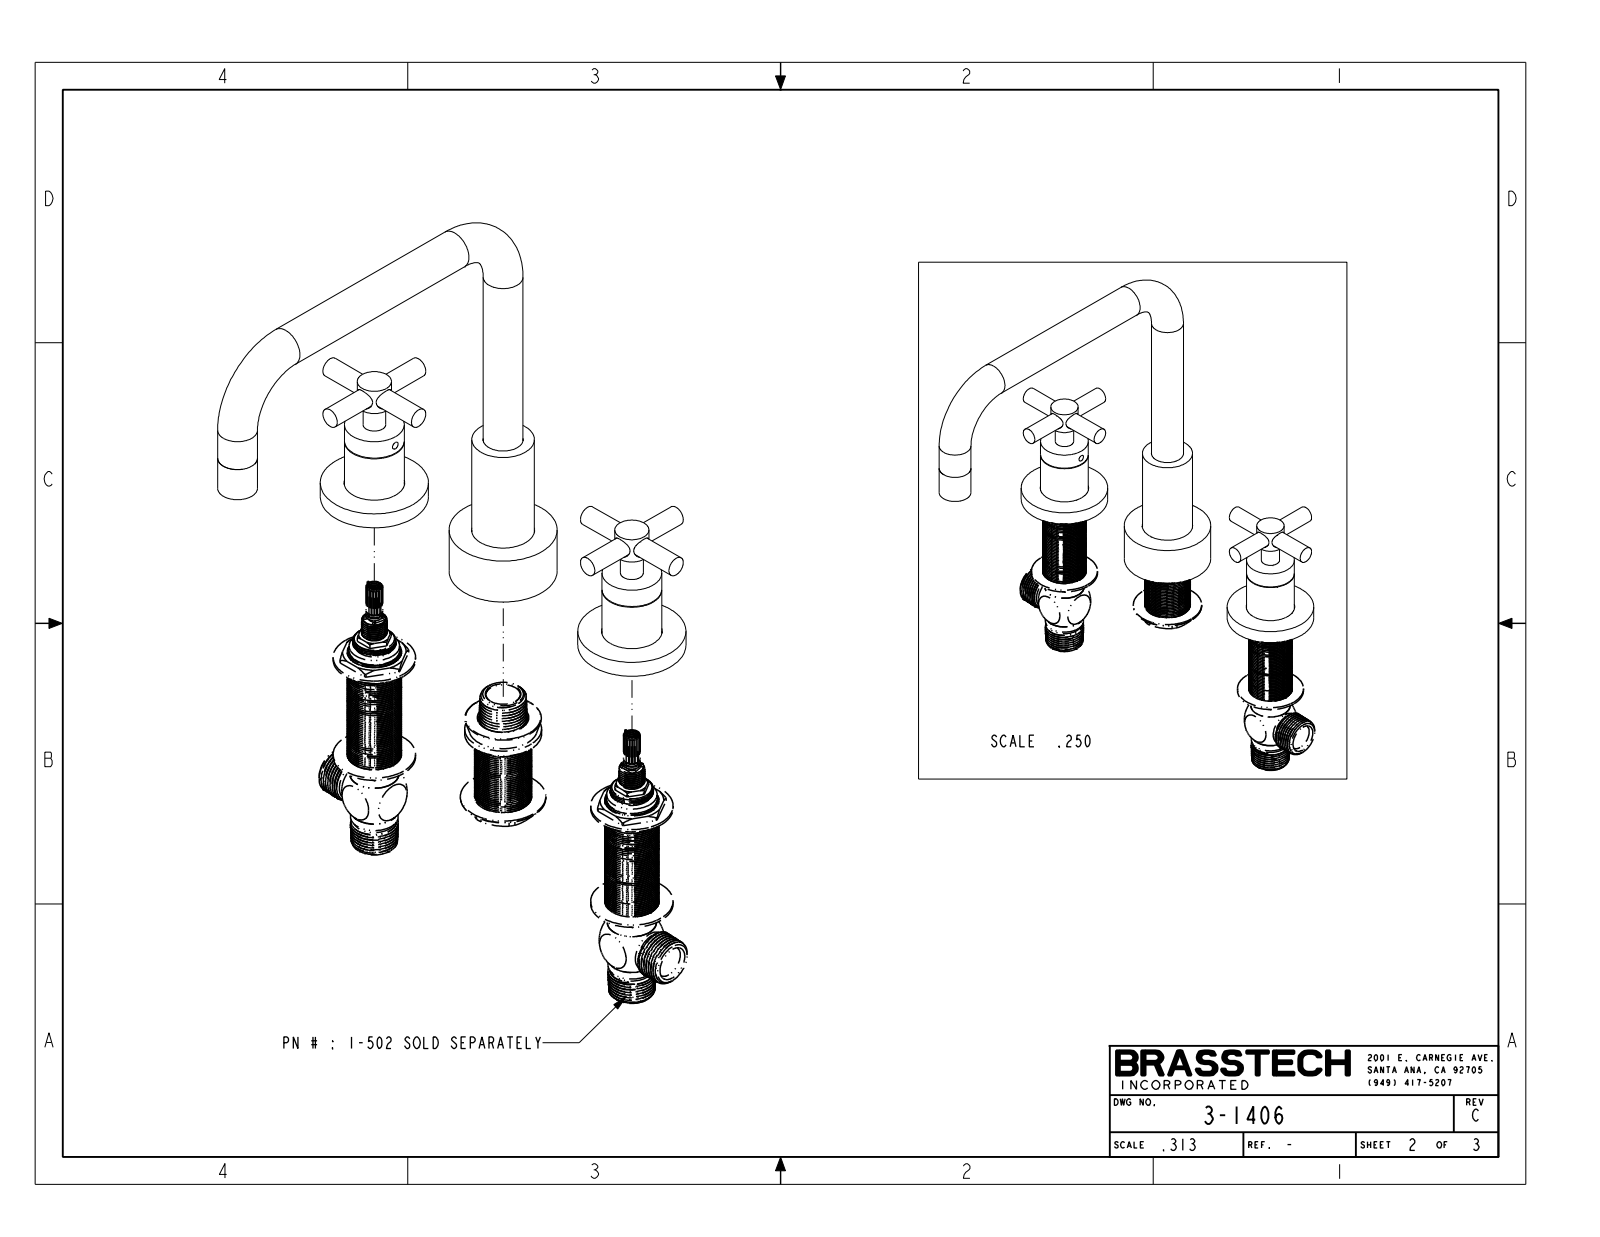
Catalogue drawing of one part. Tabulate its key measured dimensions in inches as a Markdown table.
| quantity | value |
| --- | --- |
| part name | 3-1406 |
| STEP written by | CREO PARAMETRIC BY PTC INC, 2018400 (CONFIG_CONTROL_DESIGN) |
| units | inches |
| bodies | 3 solids, 104 faces (34 planar, 66 cylindrical, 4 other) |
| overall size | 10.375 × 9.875 × 9.851 |
| volume | 27.59 in³ |
| surface area | 130.9 in² |
| round holes (diameter × count) | 0.47 × 4 |
| round bosses / shafts (diameter × count) | 0.445 × 8, 2.375 × 3, 0.875 × 3, 1.313 × 2, 0.75 × 2, 0.5 × 2, 0.4 × 2, 1.375 × 1 |
| main face-to-face distances | 0.375, 1.103, 0.728, 1.483, 1.503, 1.108, 1.128, 0.38, 0.4, 0.02 |
| hole center spacings | 5.657 |
